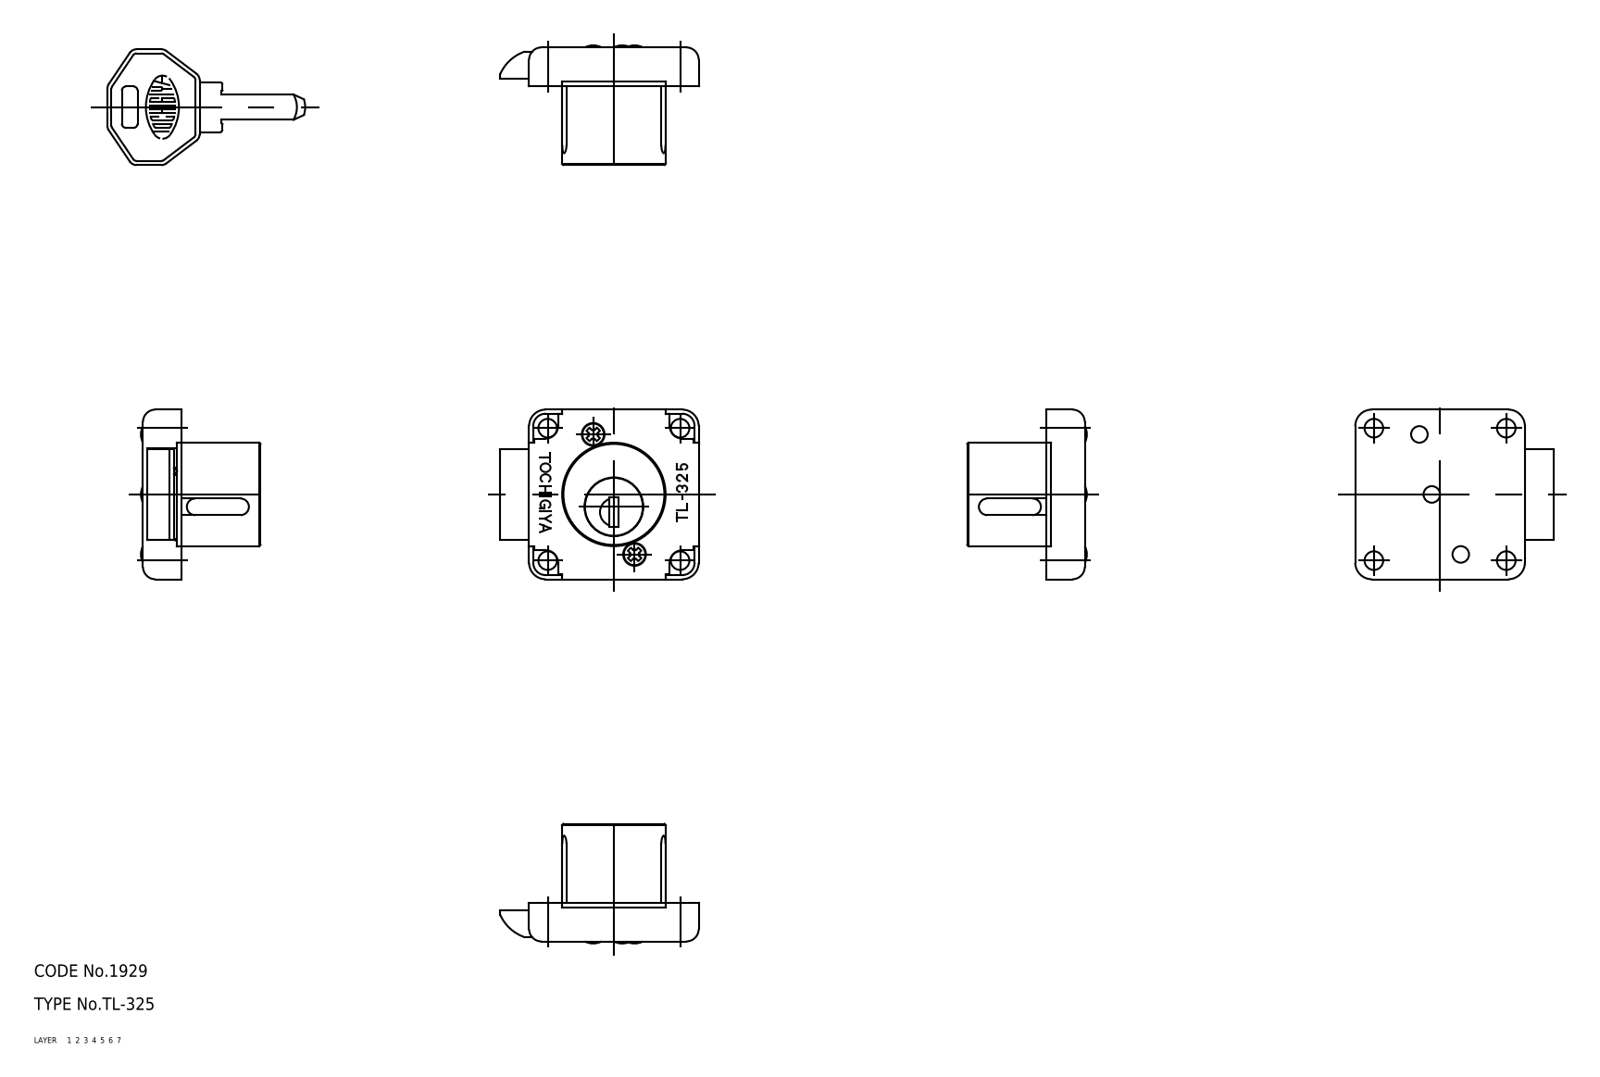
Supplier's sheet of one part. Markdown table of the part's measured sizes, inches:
| quantity | value |
| --- | --- |
| part name | collar; pin; lock; latch (+4 more) |
| STEP written by | CADfix (AUTOMOTIVE_DESIGN) |
| units | inches |
| bodies | 8 solids, 310 faces (0 planar, 0 cylindrical, 310 other) |
| overall size | 3.611 × 1.89 × 1.614 |
| volume | 1.094 in³ |
| surface area | 23.02 in² |
